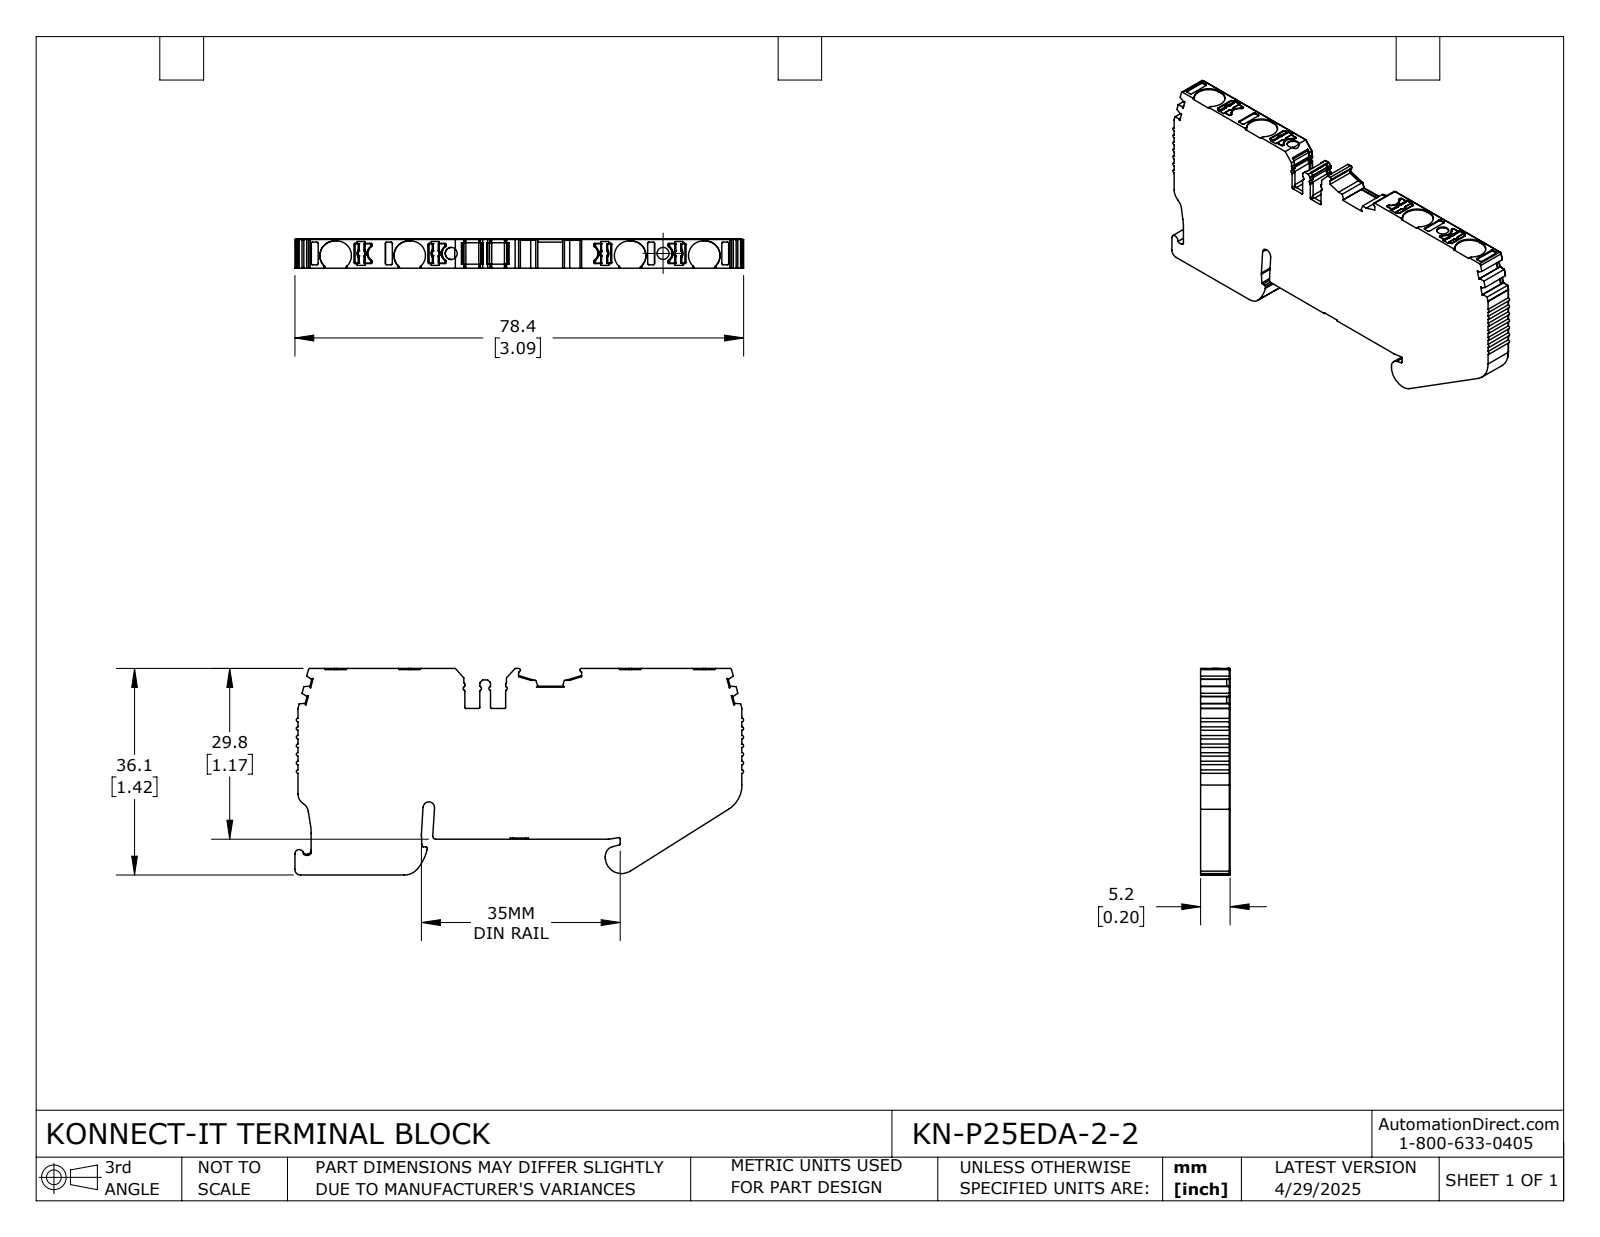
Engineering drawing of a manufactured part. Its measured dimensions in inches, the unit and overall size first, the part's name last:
Units: inches
Overall size (bounding box): 3.085 × 1.42 × 0.203
Round holes (diameter × count): ⌀0.083 ×2
Partial cylindrical surfaces — rounded edges, fillets, slot ends (radius × count): R0.008 ×78, R0.012 ×39, R0.004 ×21, R0.02 ×18, R0.006 ×16, R0.016 ×9, R0.1 ×8, R0.059 ×4
Main face-to-face distances: 0.203, 1.166, 1.174, 0.246, 1.412, 1.42, 3.052, 0.047, 0.197, 0.177
Hole centre spacings: 1.456
Volume: 0.731 in³ · Surface area: 9.637 in²
Bodies: 1 solid, 743 faces (381 planar, 291 cylindrical, 71 other)
Part name (STEP PRODUCT): KN-P25EDA-2-2
STEP written by: SolidWorks 2024 (CONFIG_CONTROL_DESIGN)
